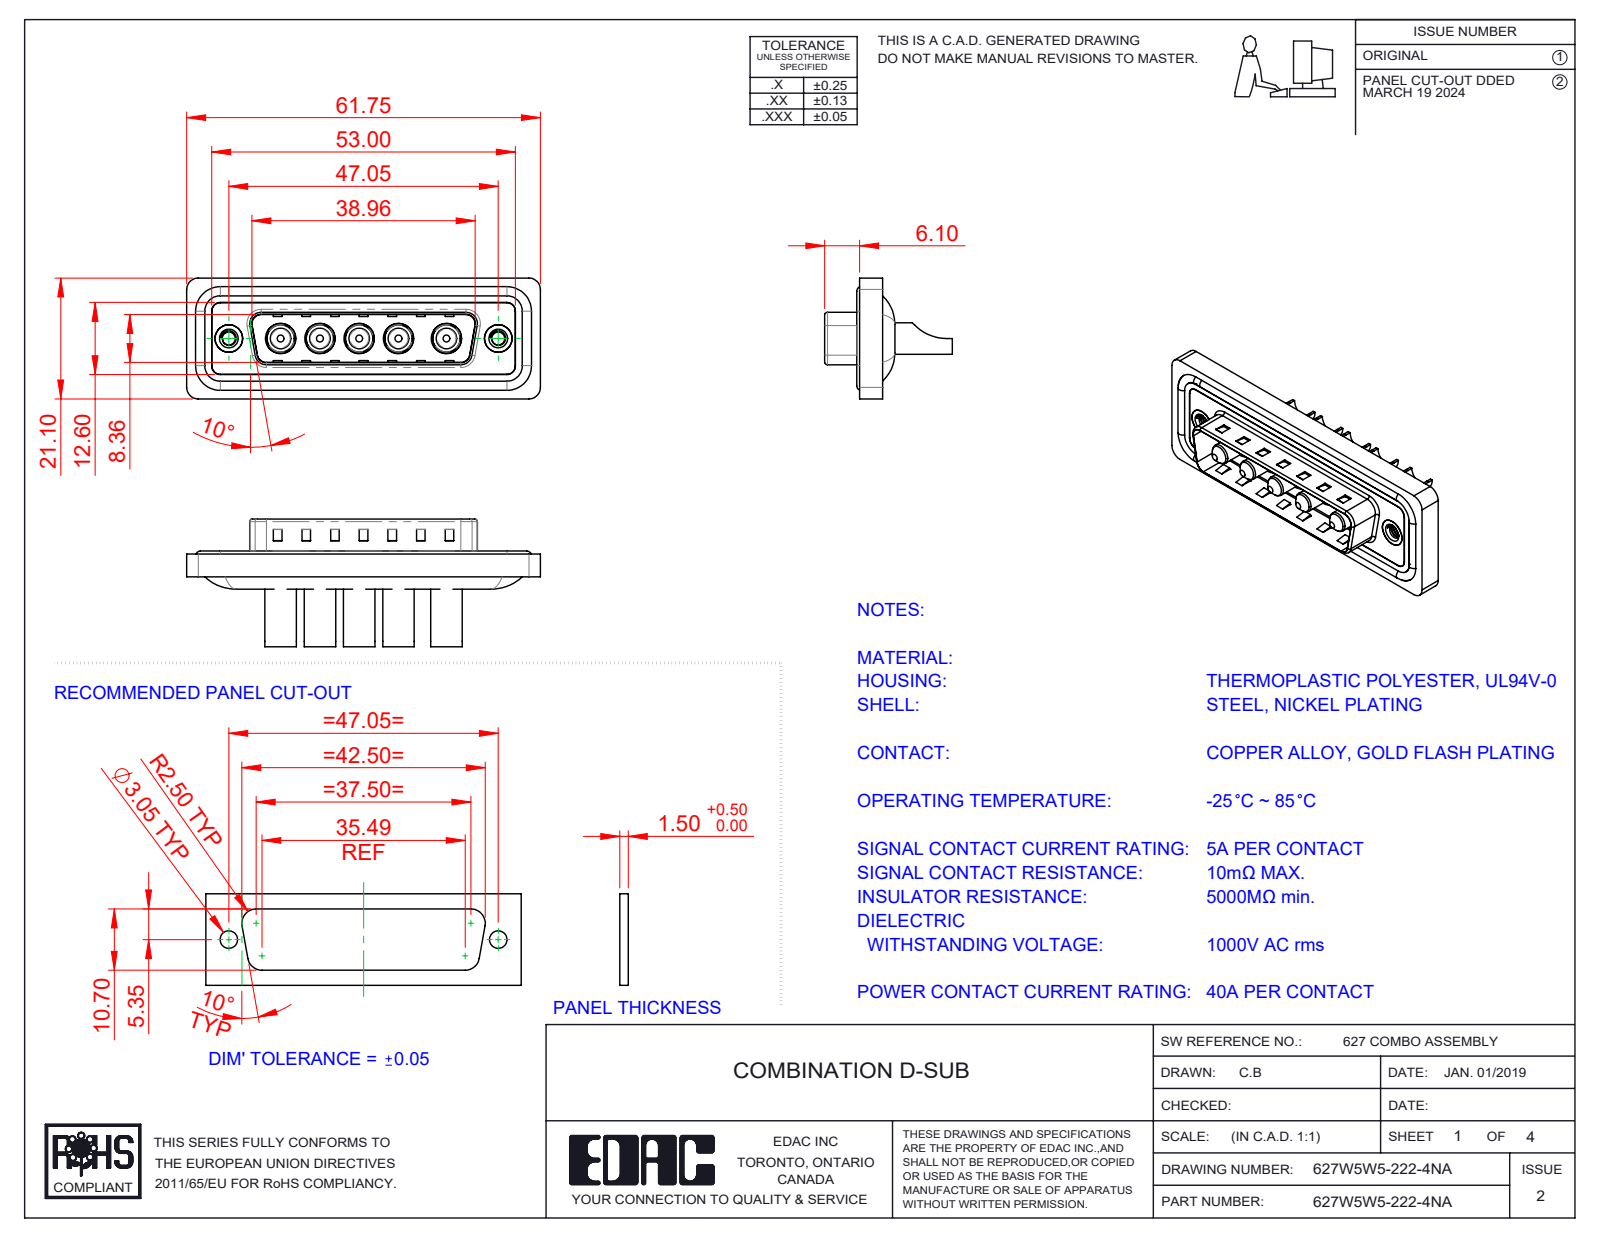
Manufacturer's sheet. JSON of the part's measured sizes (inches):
{"part_name": "Power Pin_40A SC; 627W5W5-222-4NA; 627Combo Shell Front_25 Contacts; 627Combo Waterproof Housing_25 Contacts (+3 more)", "step_written_by": "SolidWorks 2023 (CONFIG_CONTROL_DESIGN)", "units": "inches", "bodies": {"solids": 17, "faces": 696, "planar": 269, "cylindrical": 290, "other": 137}, "overall_size": [2.431, 0.878, 0.831], "volume_in3": 0.468, "surface_area_in2": 19.36, "round_holes": [[0.181, 5], [0.191, 5], [0.209, 5], [0.089, 2], [0.157, 2], [0.189, 2], [0.197, 2]], "round_bosses_or_shafts": [[0.217, 5], [0.205, 5], [0.187, 5], [0.148, 5], [0.142, 5], [0.063, 4], [0.193, 2]], "partial_cylinders_radius": [[0.059, 22], [0.079, 18], [0.02, 8], [0.063, 8], [0.083, 5], [0.01, 4], [0.024, 4], [0.026, 4]], "face_to_face_distances": [0.016, 0.02, 0.043, 0.059, 0.122, 0.063, 0.114, 0.032, 0.377, 0.222], "hole_center_spacings": [0.27, 0.356, 0.541, 1.496, 0.27, 0.33, 0.33, 0.356]}
